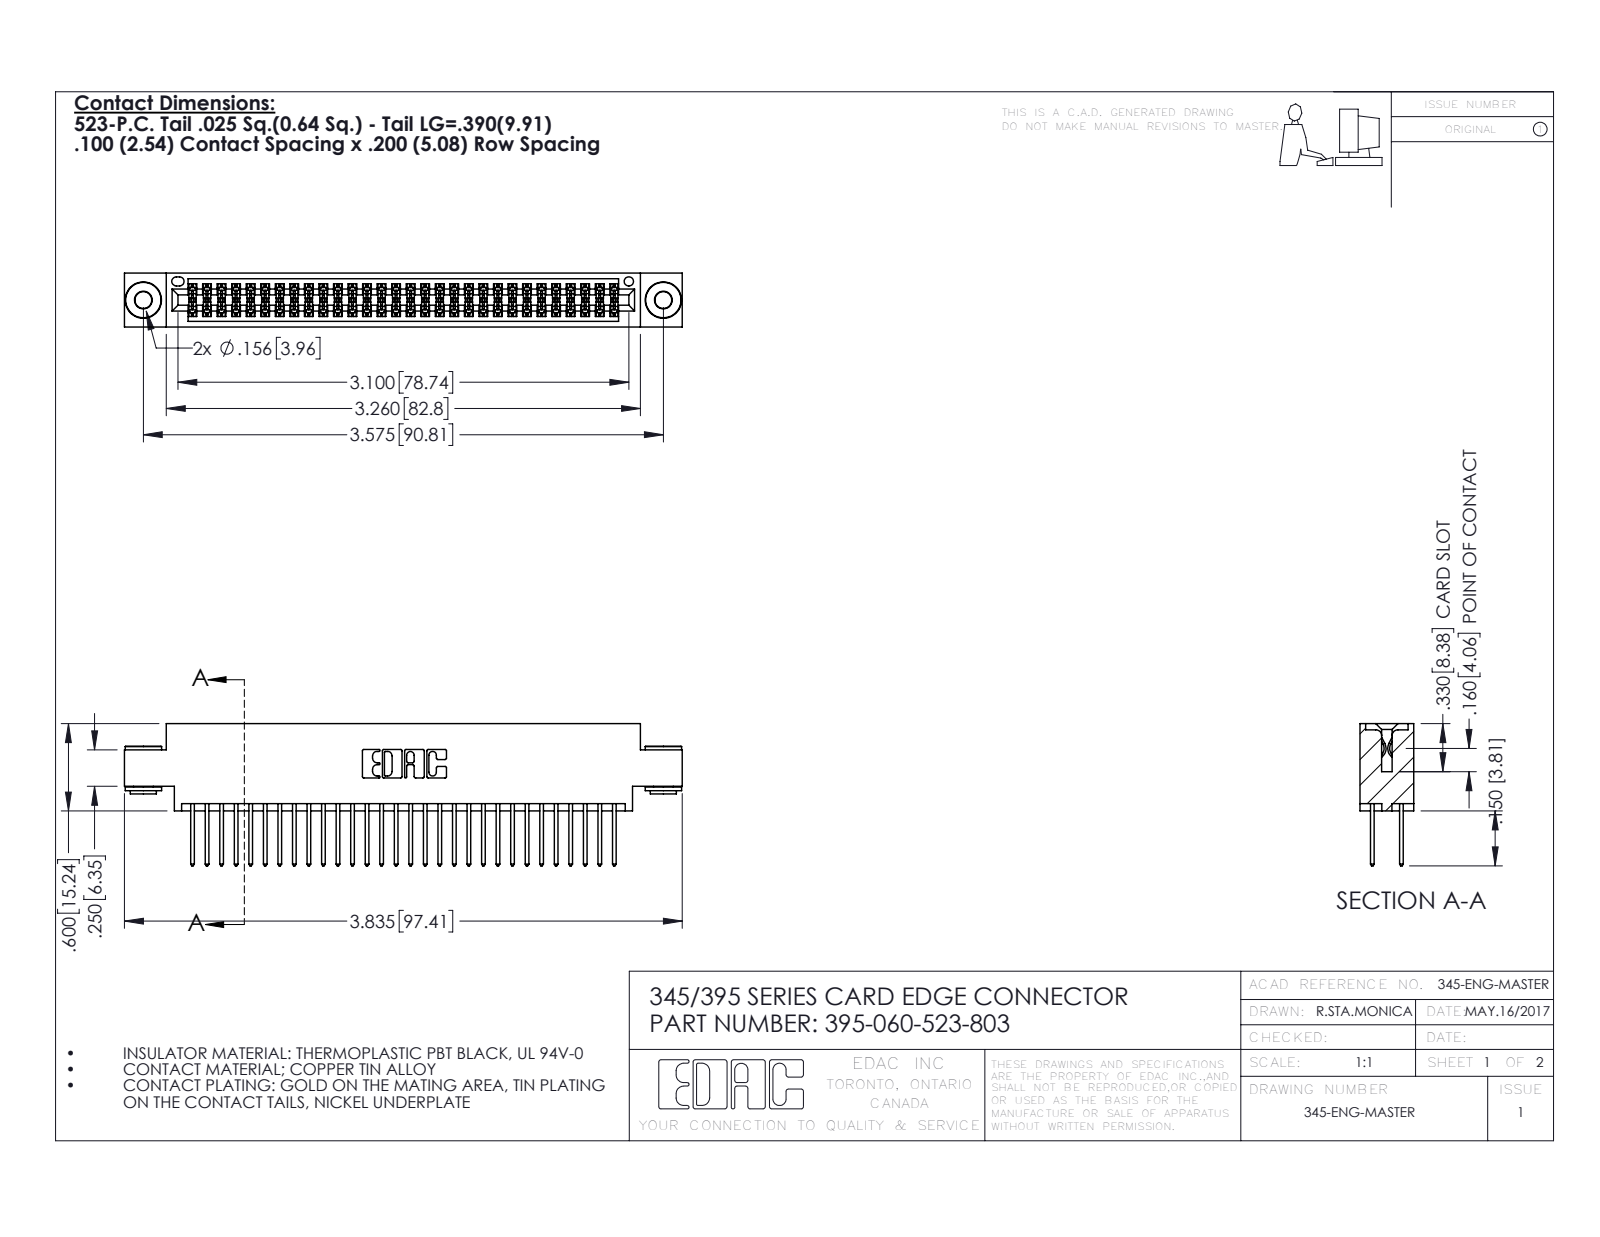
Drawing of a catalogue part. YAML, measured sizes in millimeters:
part_name: "345 Part_0.170 Offset - 0.156 Dia-TH; 395-060-523-803; 345-292-001_345-293-123; 345-250-002_345-250-002-102"
step_written_by: "SolidWorks 2016 (CONFIG_CONTROL_DESIGN)"
units: millimeters
bodies: {solids: 63, faces: 3168, planar: 2074, cylindrical: 1086, other: 8}
overall_size: [97.4, 24.8, 9.4]
volume: 9370
surface_area: 14540
round_holes:
  - {diameter: 2.9, count: 2}
  - {diameter: 4, count: 2}
  - {diameter: 1.6, count: 1}
round_bosses_or_shafts:
  - {diameter: 6.4, count: 2}
  - {diameter: 4.6, count: 2}
  - {diameter: 3.5, count: 2}
partial_cylinders:
  - {radius: 0.2, count: 90}
  - {radius: 0.3, count: 60}
  - {radius: 0.3, count: 22}
  - {radius: 0.2, count: 6}
  - {radius: 0.8, count: 6}
  - {radius: 0.7, count: 3}
  - {radius: 0.4, count: 2}
  - {radius: 0.5, count: 2}
face_to_face_distances: [1.8, 7.6, 5.1, 2.5, 6.9, 0.6, 9.4, 5.7, 4.4, 3.8]
hole_center_spacings: [6.9, 84.8, 90.8]
